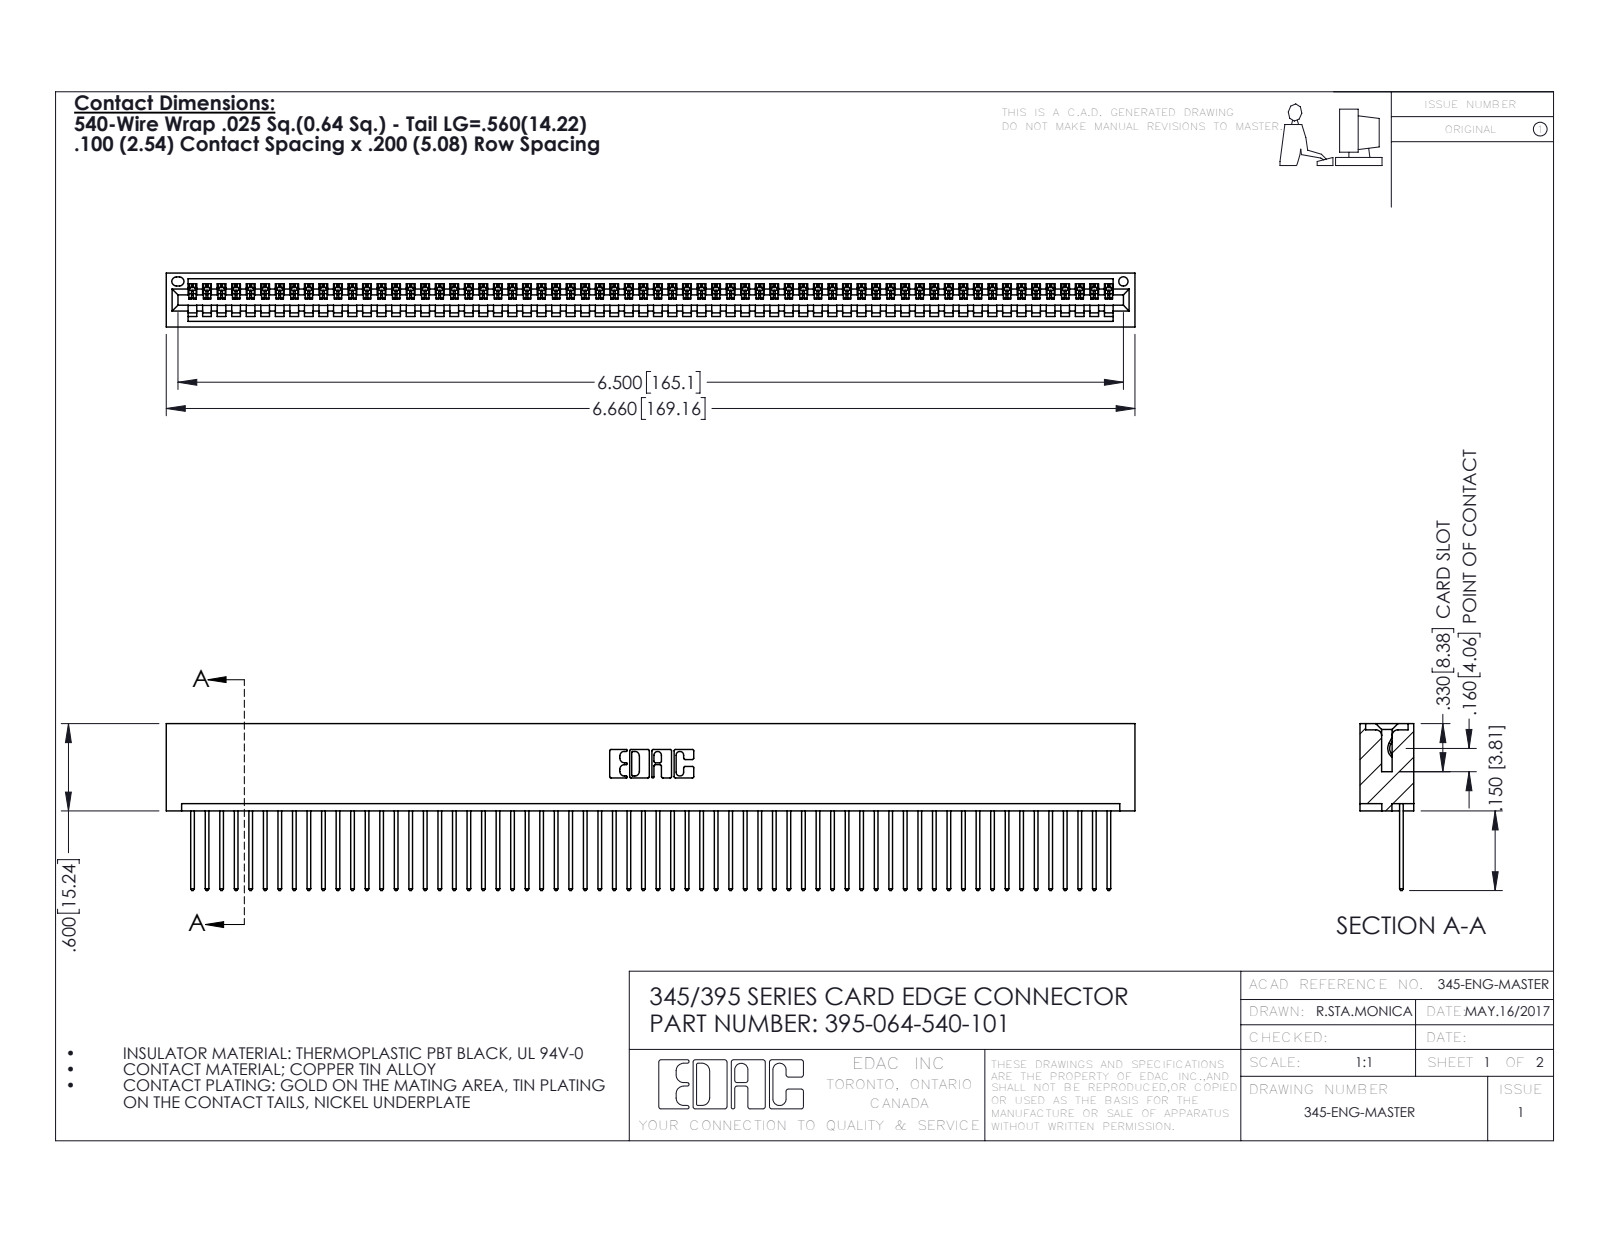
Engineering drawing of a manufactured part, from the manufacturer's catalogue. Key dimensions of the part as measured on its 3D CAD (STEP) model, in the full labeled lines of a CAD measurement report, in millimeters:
Part name (STEP PRODUCT): 395-064-540-101; 345-292-001_345-293-140; 345 Part_No Mounting Lugs
STEP written by: SolidWorks 2016 (CONFIG_CONTROL_DESIGN)
Units: millimetres
Bodies: 65 solids, 3830 faces (2636 planar, 1194 cylindrical, 0 other)
Overall size (bounding box): 169.2 × 29.1 × 9.4
Volume: 16 910 mm³ · Surface area: 23 590 mm²
Round holes (diameter × count): ⌀1.6 ×1
Partial cylindrical surfaces — rounded edges, fillets, slot ends (radius × count): R0.2 ×128, R0.3 ×128, R0.3 ×22, R0.2 ×6, R0.8 ×6, R0.7 ×3, R0.8 ×2, R1 ×2
Main face-to-face distances: 1.8, 7.6, 2.5, 6.9, 0.6, 9.4, 5.1, 5.7, 3.8, 1.8
